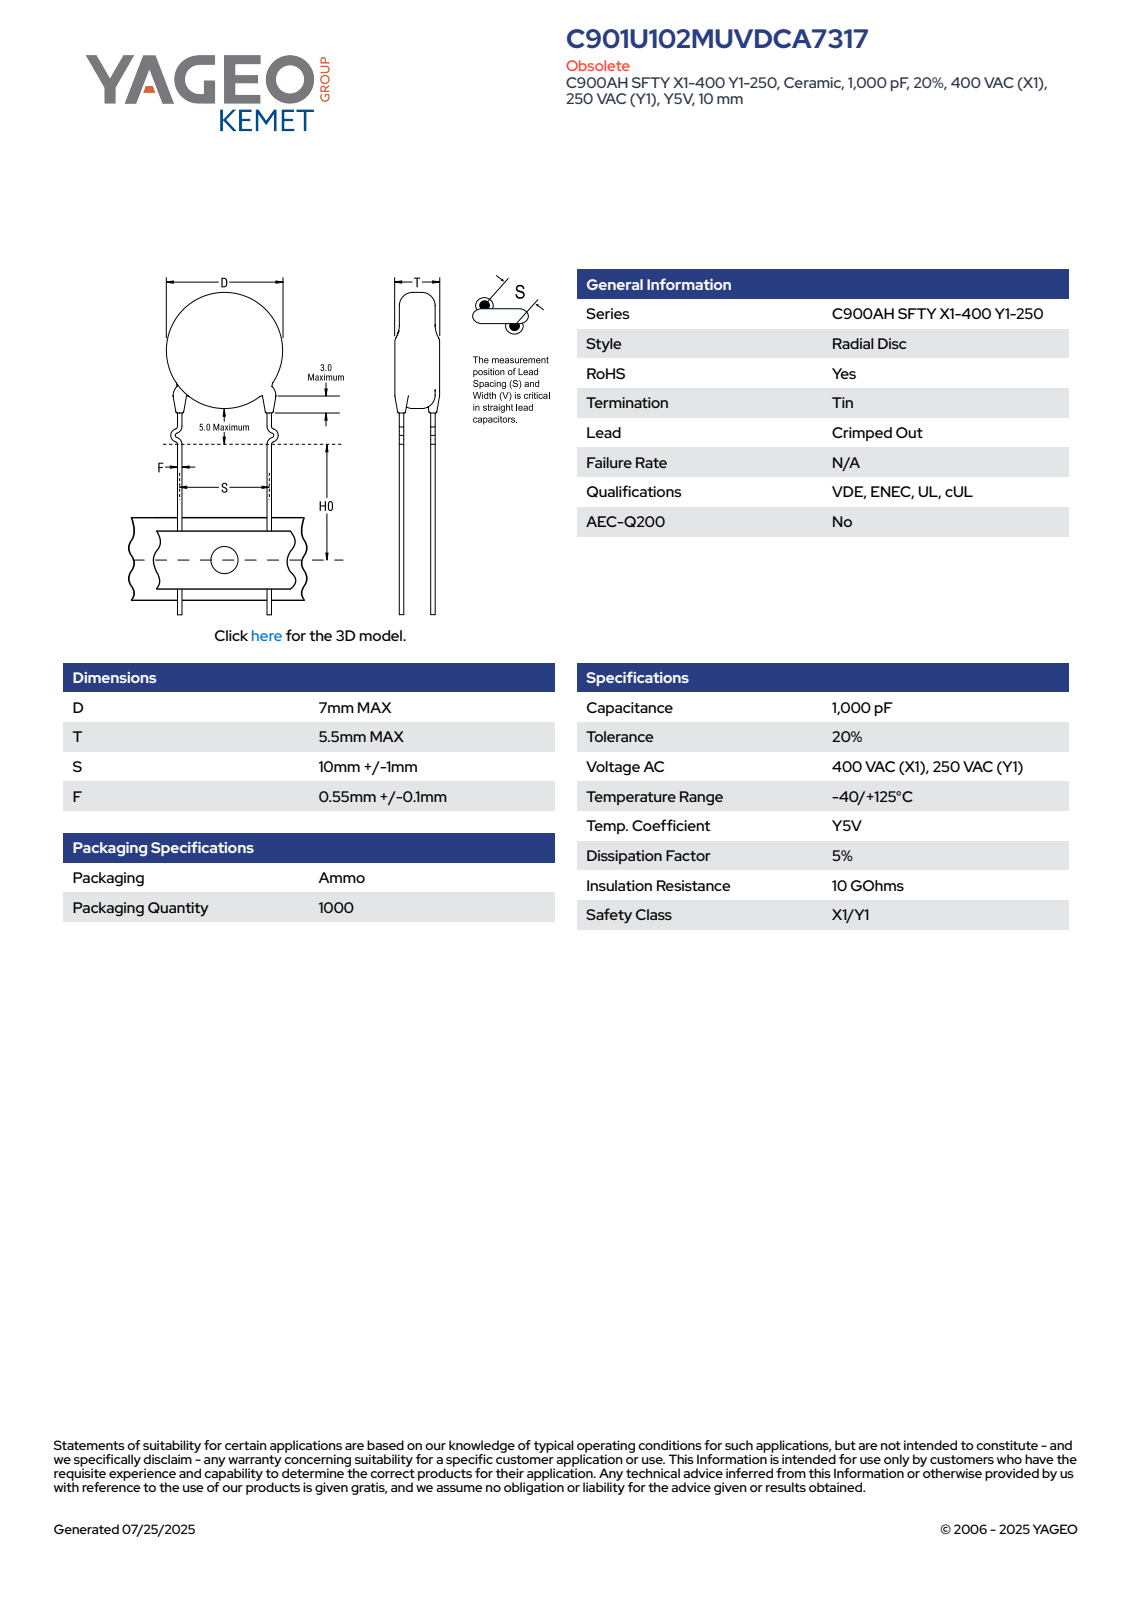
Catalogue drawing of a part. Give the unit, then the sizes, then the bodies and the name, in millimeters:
Units: millimetres
Overall size (bounding box): 32 × 13.59 × 7.28
Round bosses / shafts (diameter × count): ⌀1.2 ×4, ⌀7 ×1
Main face-to-face distances: 5.5, 0.73, 3.87, 3.14, 0.59, 0.32, 2.97, 1.5, 2.16, 2.24
Volume: 228 mm³ · Surface area: 316 mm²
Bodies: 4 solids, 93 faces (63 planar, 10 cylindrical, 20 other)
Part name (STEP PRODUCT): CCD_KCOC900_D7T5.5S10LL20F0.55
STEP written by: SolidWorks 2014 (AUTOMOTIVE_DESIGN)
